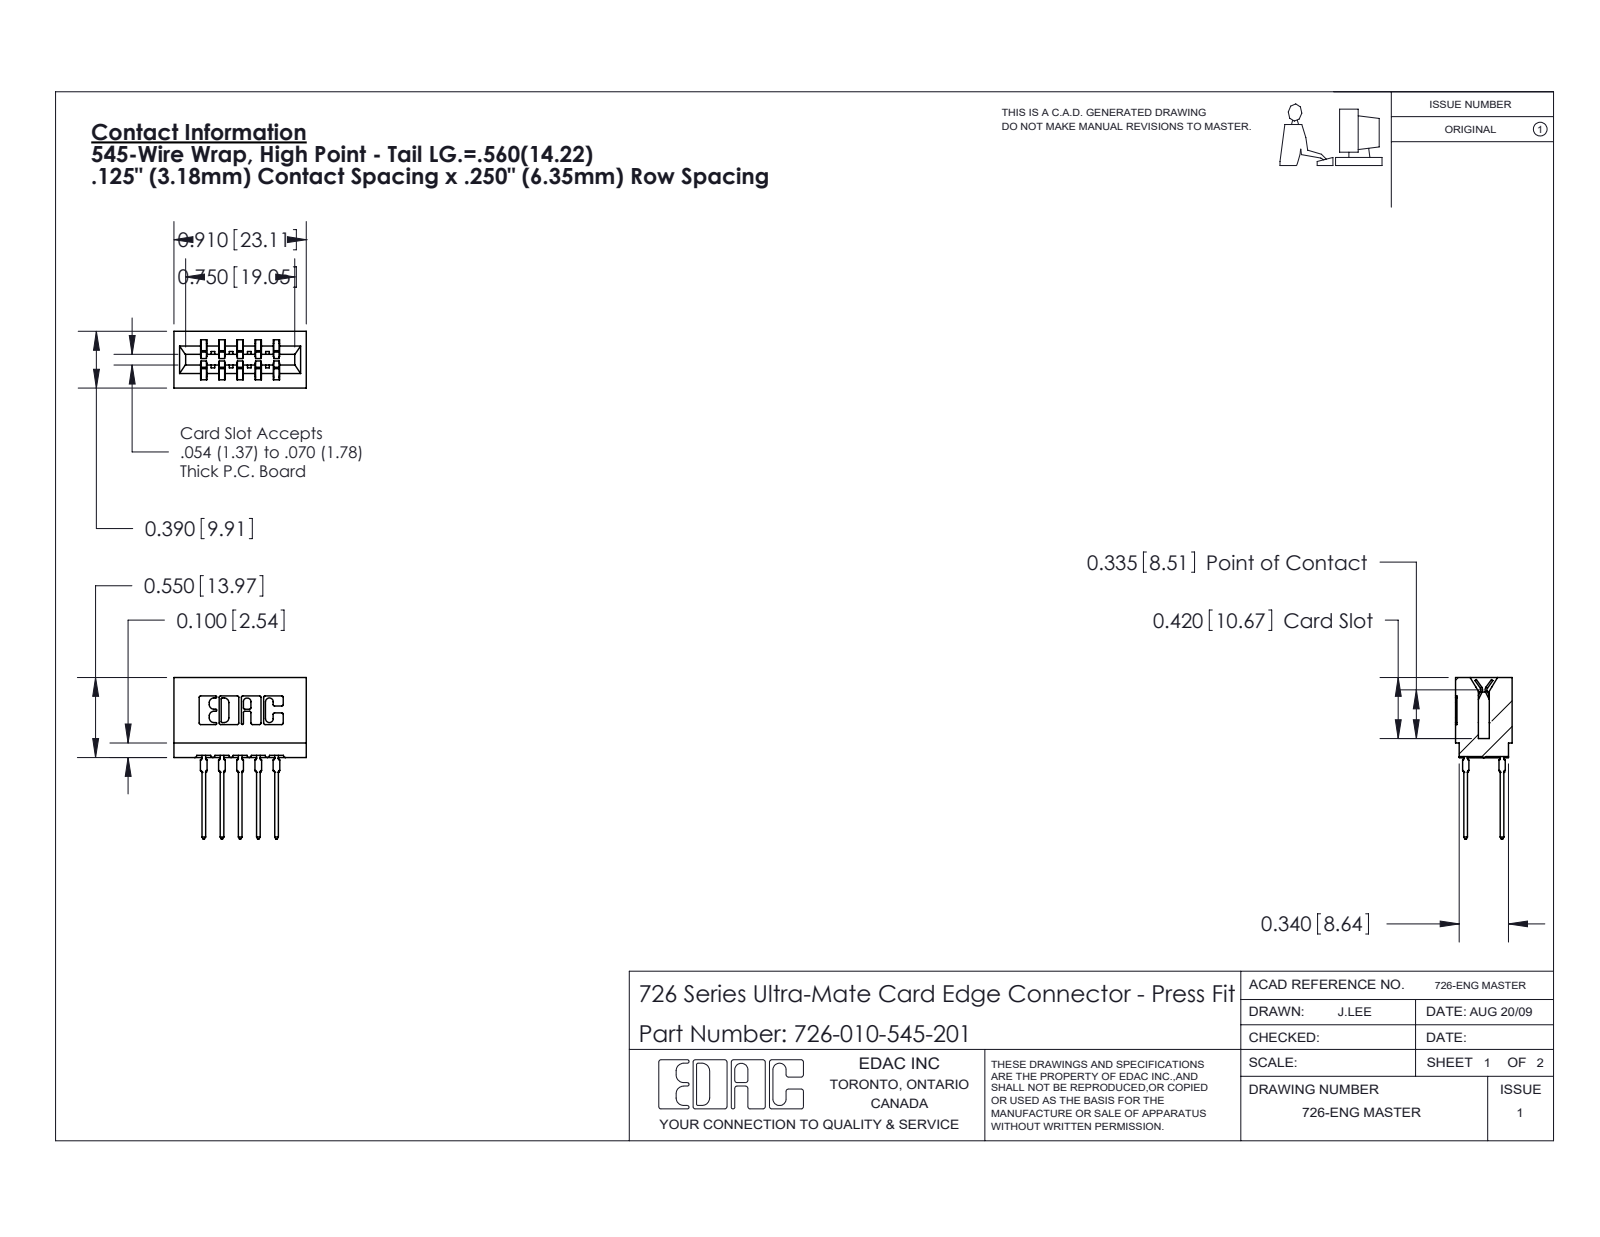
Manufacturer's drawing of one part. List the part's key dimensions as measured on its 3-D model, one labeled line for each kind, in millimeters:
Part name (STEP PRODUCT): 726 Part_.515 Slot Depth - 01; 746-292-001_545; 726-010-545-201
STEP written by: SolidWorks 2020 (CONFIG_CONTROL_DESIGN)
Units: millimetres
Bodies: 11 solids, 992 faces (515 planar, 217 cylindrical, 260 other)
Overall size (bounding box): 28.2 × 23.1 × 9.9
Volume: 2 360 mm³ · Surface area: 3 432 mm²
Partial cylindrical surfaces — rounded edges, fillets, slot ends (radius × count): R0.3 ×22, R0.5 ×20, R0.1 ×8, R0.3 ×8, R0.2 ×6, R0.4 ×6, R0.8 ×6, R0.7 ×3
Main face-to-face distances: 6.4, 1.4, 8.5, 1.1, 3.2, 3.2, 0.6, 2.1, 7.8, 9.9
